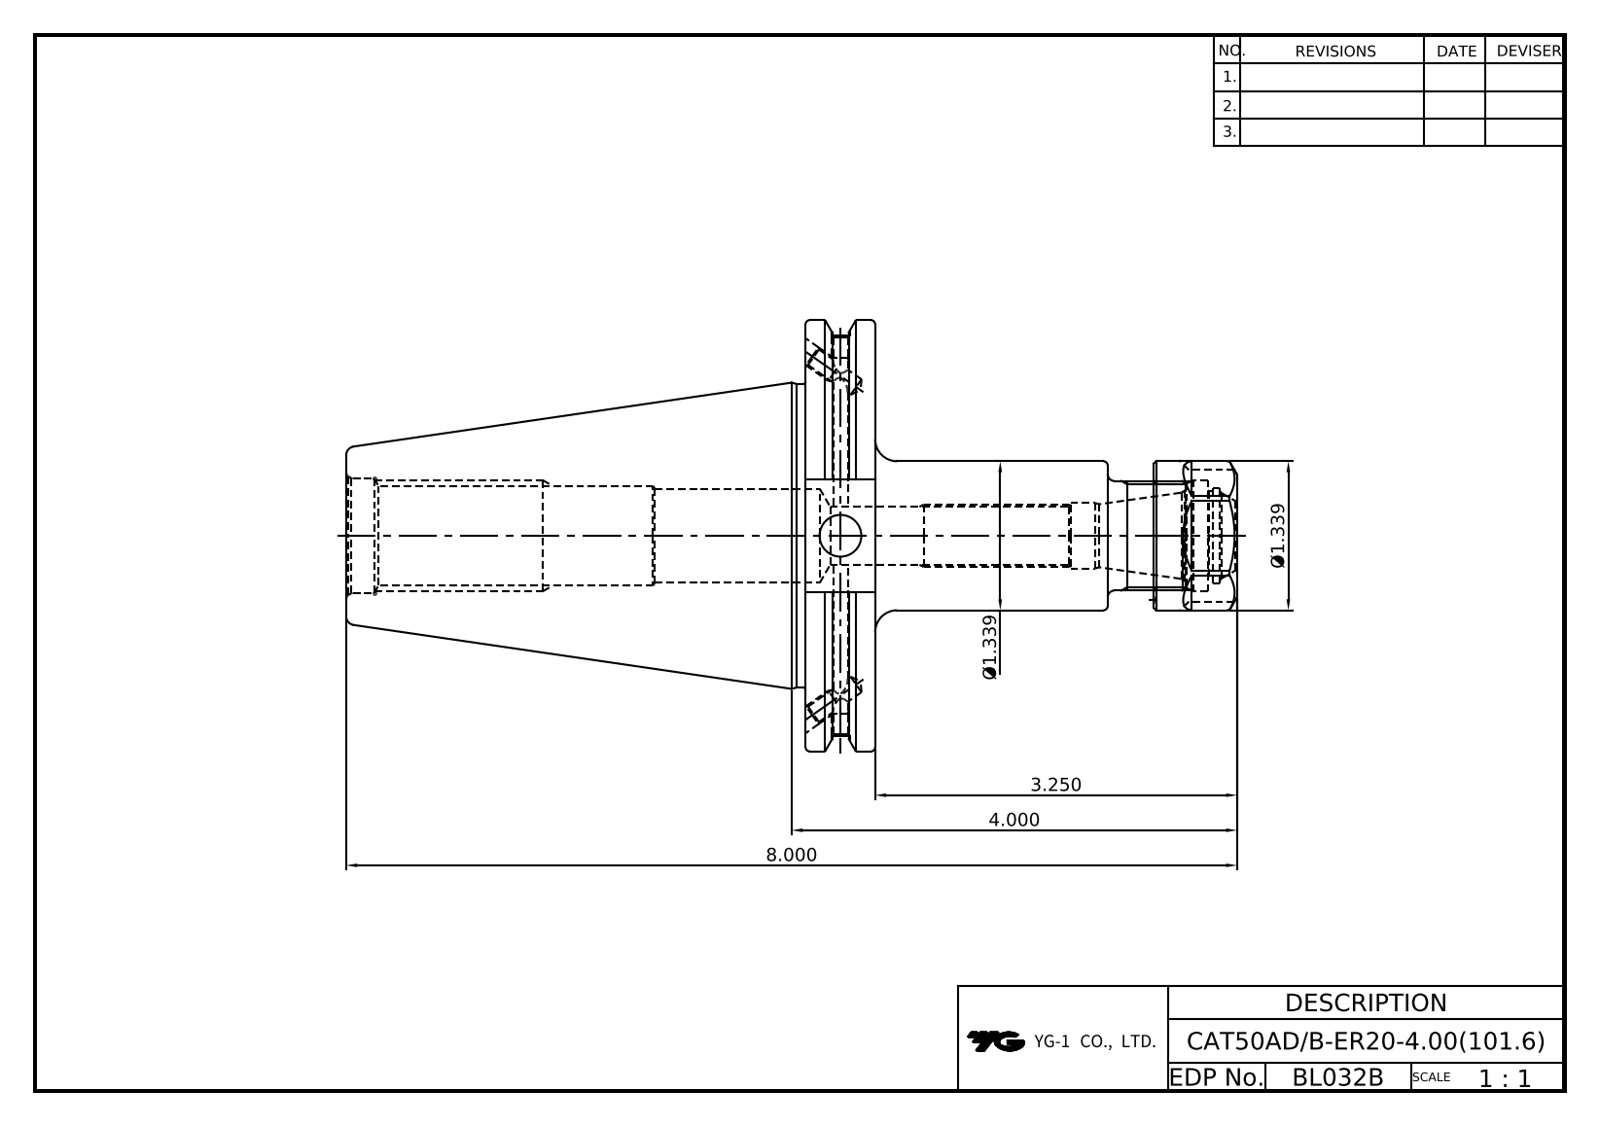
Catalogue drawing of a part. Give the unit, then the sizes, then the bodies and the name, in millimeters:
Units: millimetres
Overall size (bounding box): 203.2 × 98.42 × 94.69
Round holes (diameter × count): ⌀3.24 ×2, ⌀4.13 ×2, ⌀4.2 ×2, ⌀5 ×2, ⌀9.53 ×1, ⌀12.57 ×1, ⌀14.9 ×1, ⌀16 ×1, ⌀18.4 ×1, ⌀21.76 ×1, ⌀21.97 ×1, ⌀23.5 ×1
Round bosses / shafts (diameter × count): ⌀98.42 ×1, ⌀91.29 ×1, ⌀69.25 ×1, ⌀34 ×1, ⌀25 ×1
Main face-to-face distances: 15.88, 104.77, 120.65, 30, 203.2, 98.43, 82.55, 19, 184.2, 79.43
Volume: 374 420 mm³ · Surface area: 60 396 mm²
Bodies: 2 solids, 117 faces (56 planar, 33 cylindrical, 28 other)
Part name (STEP PRODUCT): LO-CAT50ADB-ER20-4.00; ER20NUT
STEP written by: Autodesk Inventor 2024 (AUTOMOTIVE_DESIGN)
